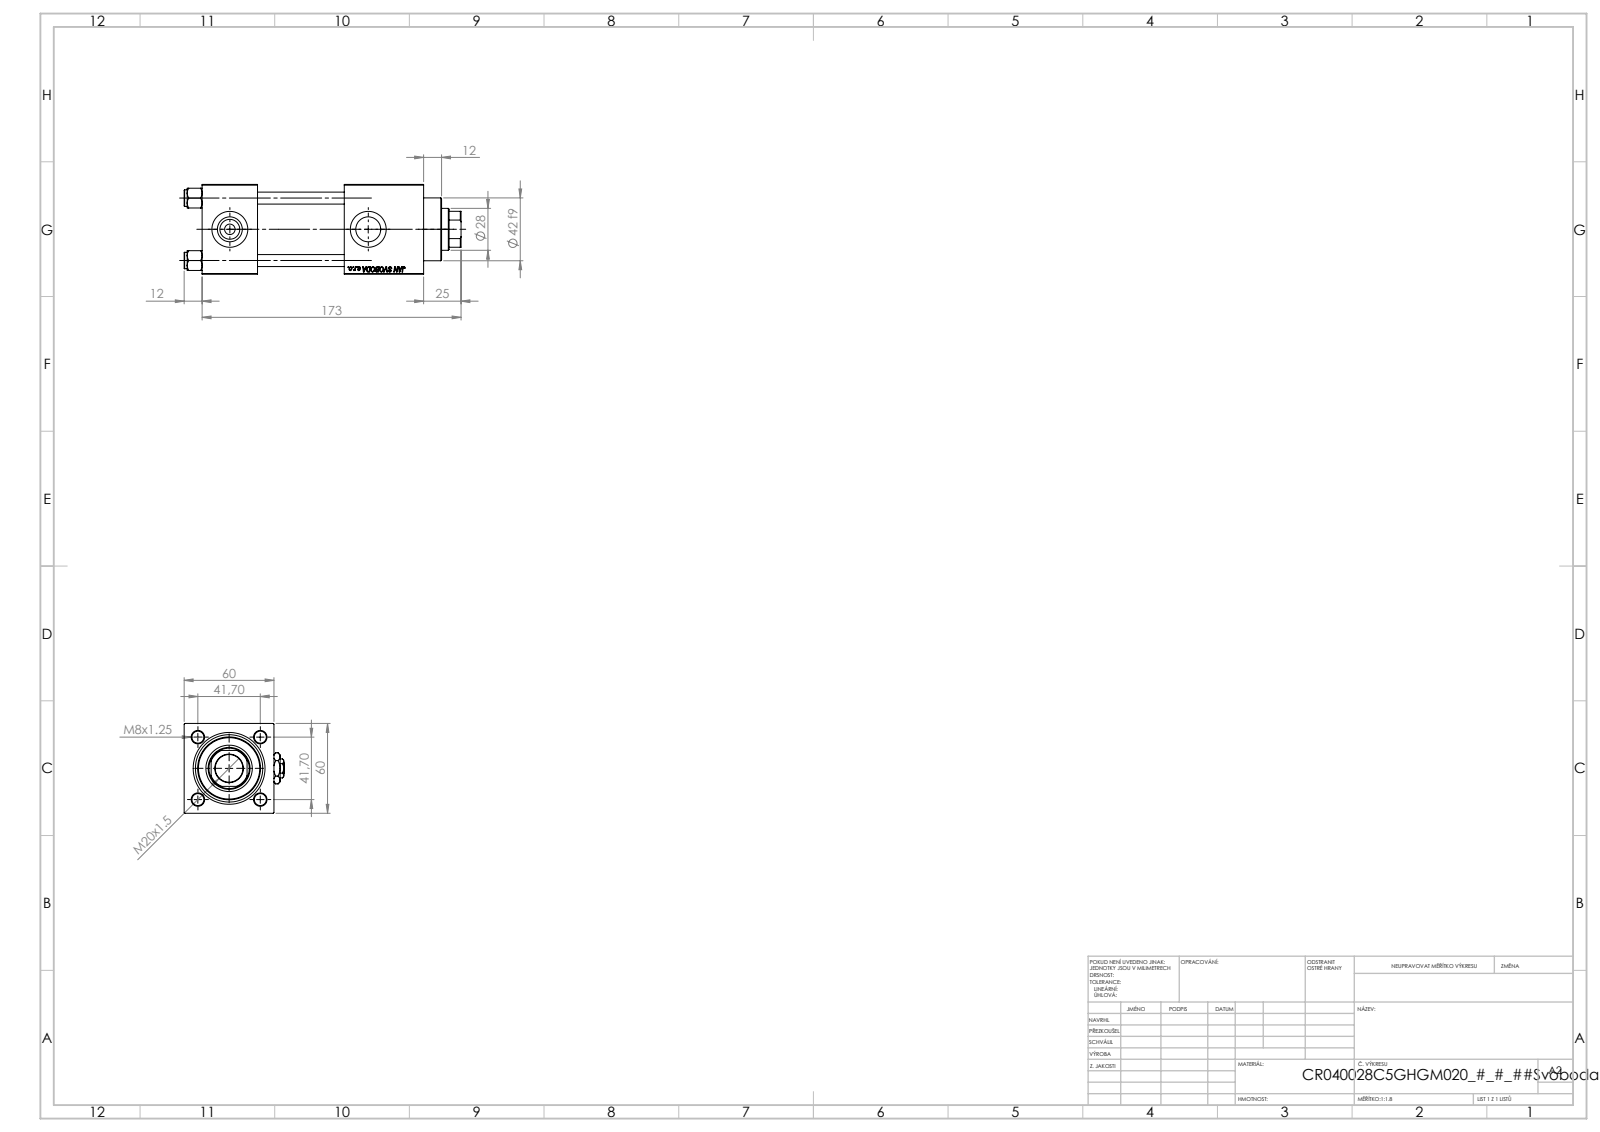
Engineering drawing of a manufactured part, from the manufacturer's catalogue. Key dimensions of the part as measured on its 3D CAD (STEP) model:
Part name (STEP PRODUCT): V215_VC_A; V215CR_C_Body; Zatka_pro_OIL_PORT; V215CR_VCP_C (+2 more)
STEP written by: SolidWorks 2019 (CONFIG_CONTROL_DESIGN)
Units: millimetres
Bodies: 12 solids, 1202 faces (550 planar, 94 cylindrical, 558 other)
Overall size (bounding box): 185 × 67 × 60
Volume: 422 827 mm³ · Surface area: 113 084 mm²
Round holes (diameter × count): ⌀8 ×4, ⌀7 ×2, ⌀16.66 ×2, ⌀24 ×2, ⌀18.5 ×1, ⌀28 ×1, ⌀31 ×1, ⌀40 ×1, ⌀45 ×1
Round bosses / shafts (diameter × count): ⌀11 ×4, ⌀46 ×1, ⌀42 ×1
Partial cylindrical surfaces — rounded edges, fillets, slot ends (radius × count): R13.5 ×1
Main face-to-face distances: 60, 37, 58, 95, 53, 119.3, 82.3, 24.3, 148, 111
Hole centre spacings: 29.49, 41.7, 58.97, 92.5
